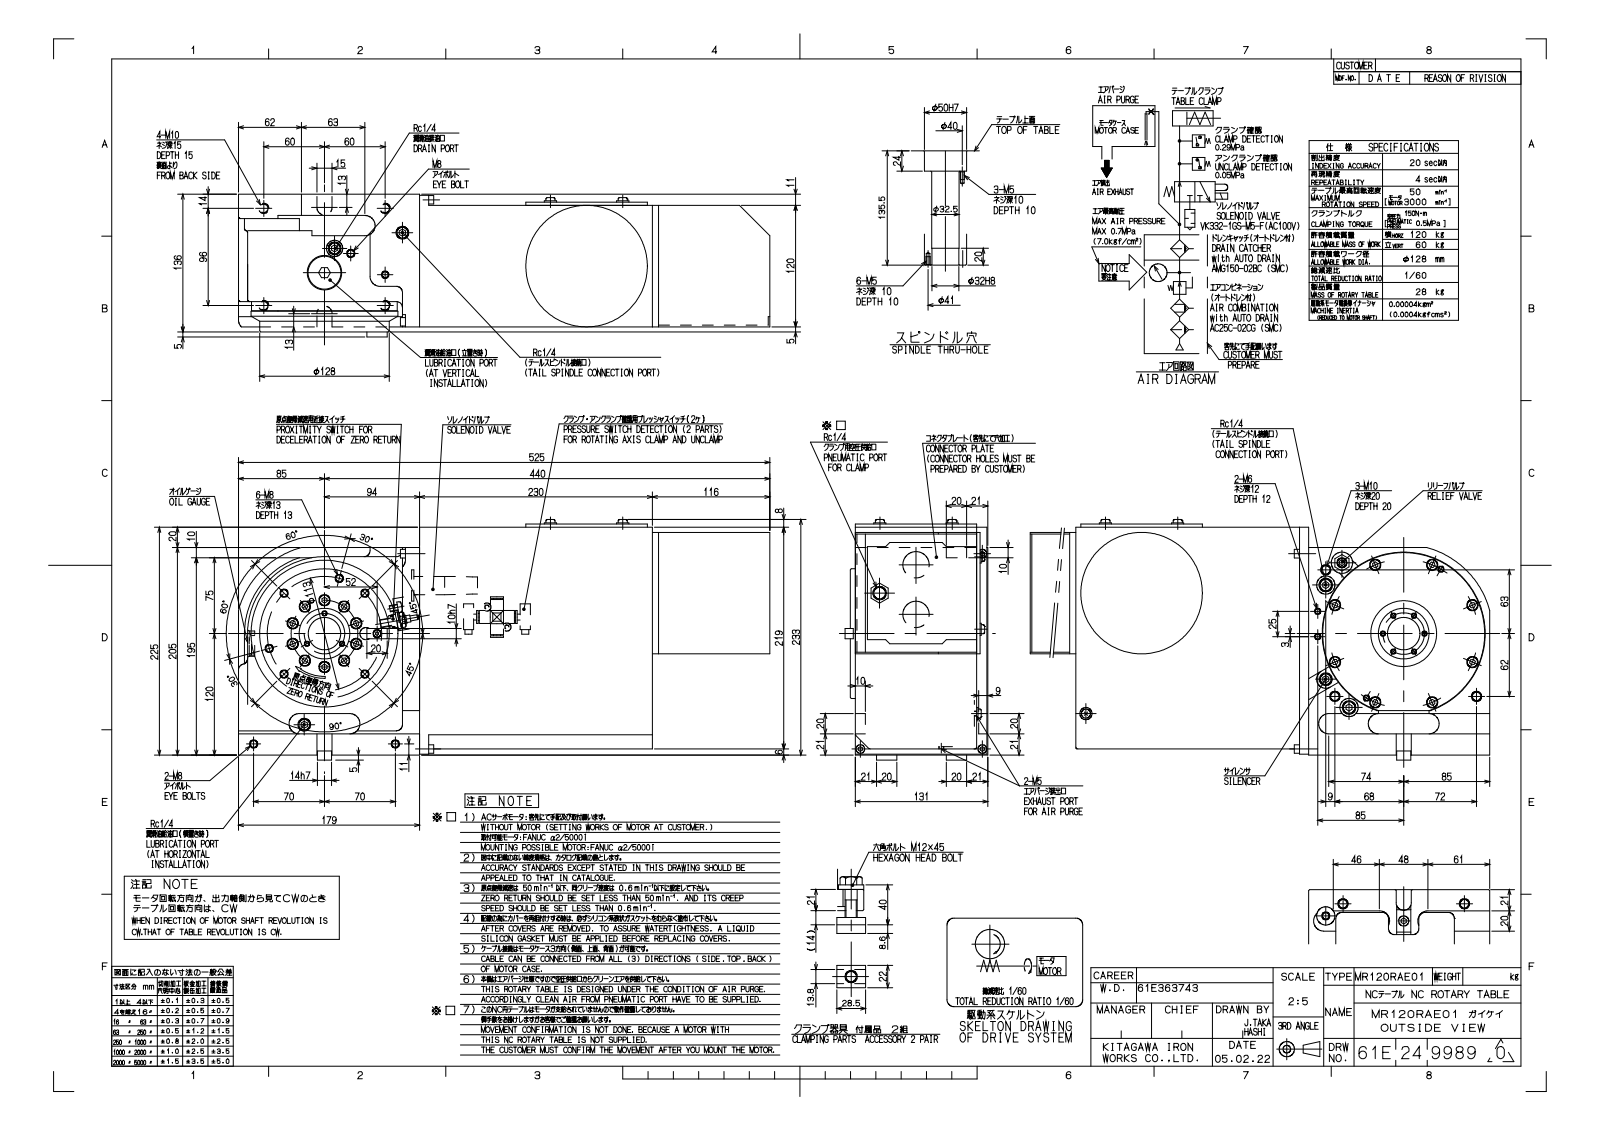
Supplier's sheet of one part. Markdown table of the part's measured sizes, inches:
| quantity | value |
| --- | --- |
| part name | MR120RAY01 |
| STEP written by | ST-DEVELOPER v16.7 (AUTOMOTIVE_DESIGN) |
| units | inches |
| bodies | 1 solid, 788 faces (434 planar, 256 cylindrical, 98 other) |
| overall size | 13.335 × 10.315 × 9.685 |
| volume | 498.9 in³ |
| surface area | 690.4 in² |
| round holes (diameter × count) | 0.433 × 18, 0.268 × 9, 0.315 × 9, 0.335 × 7, 0.197 × 5, 0.421 × 5, 0.394 × 4, 0.165 × 3, 0.236 × 2, 0.709 × 2, 0.217 × 1, 0.24 × 1 |
| round bosses / shafts (diameter × count) | 0.335 × 6, 0.472 × 4, 0.354 × 4, 0.276 × 4, 5.709 × 1, 5.669 × 1, 5.039 × 1, 4.724 × 1 |
| partial cylindrical surfaces (radius × count) | 0.236 × 17, 0.394 × 10, 0.295 × 2, 0.276 × 1, 0.354 × 1, 1.575 × 1, 2.992 × 1, 3.11 × 1 |
| main face-to-face distances | 0.197, 0.063, 4.724, 0.236, 4.921, 4.661, 0.984, 5.157, 5.138, 0.394 |
| hole center spacings | 1.299, 1.195, 2.102, 2.215, 2.471, 2.894, 2.898, 4.093 |
